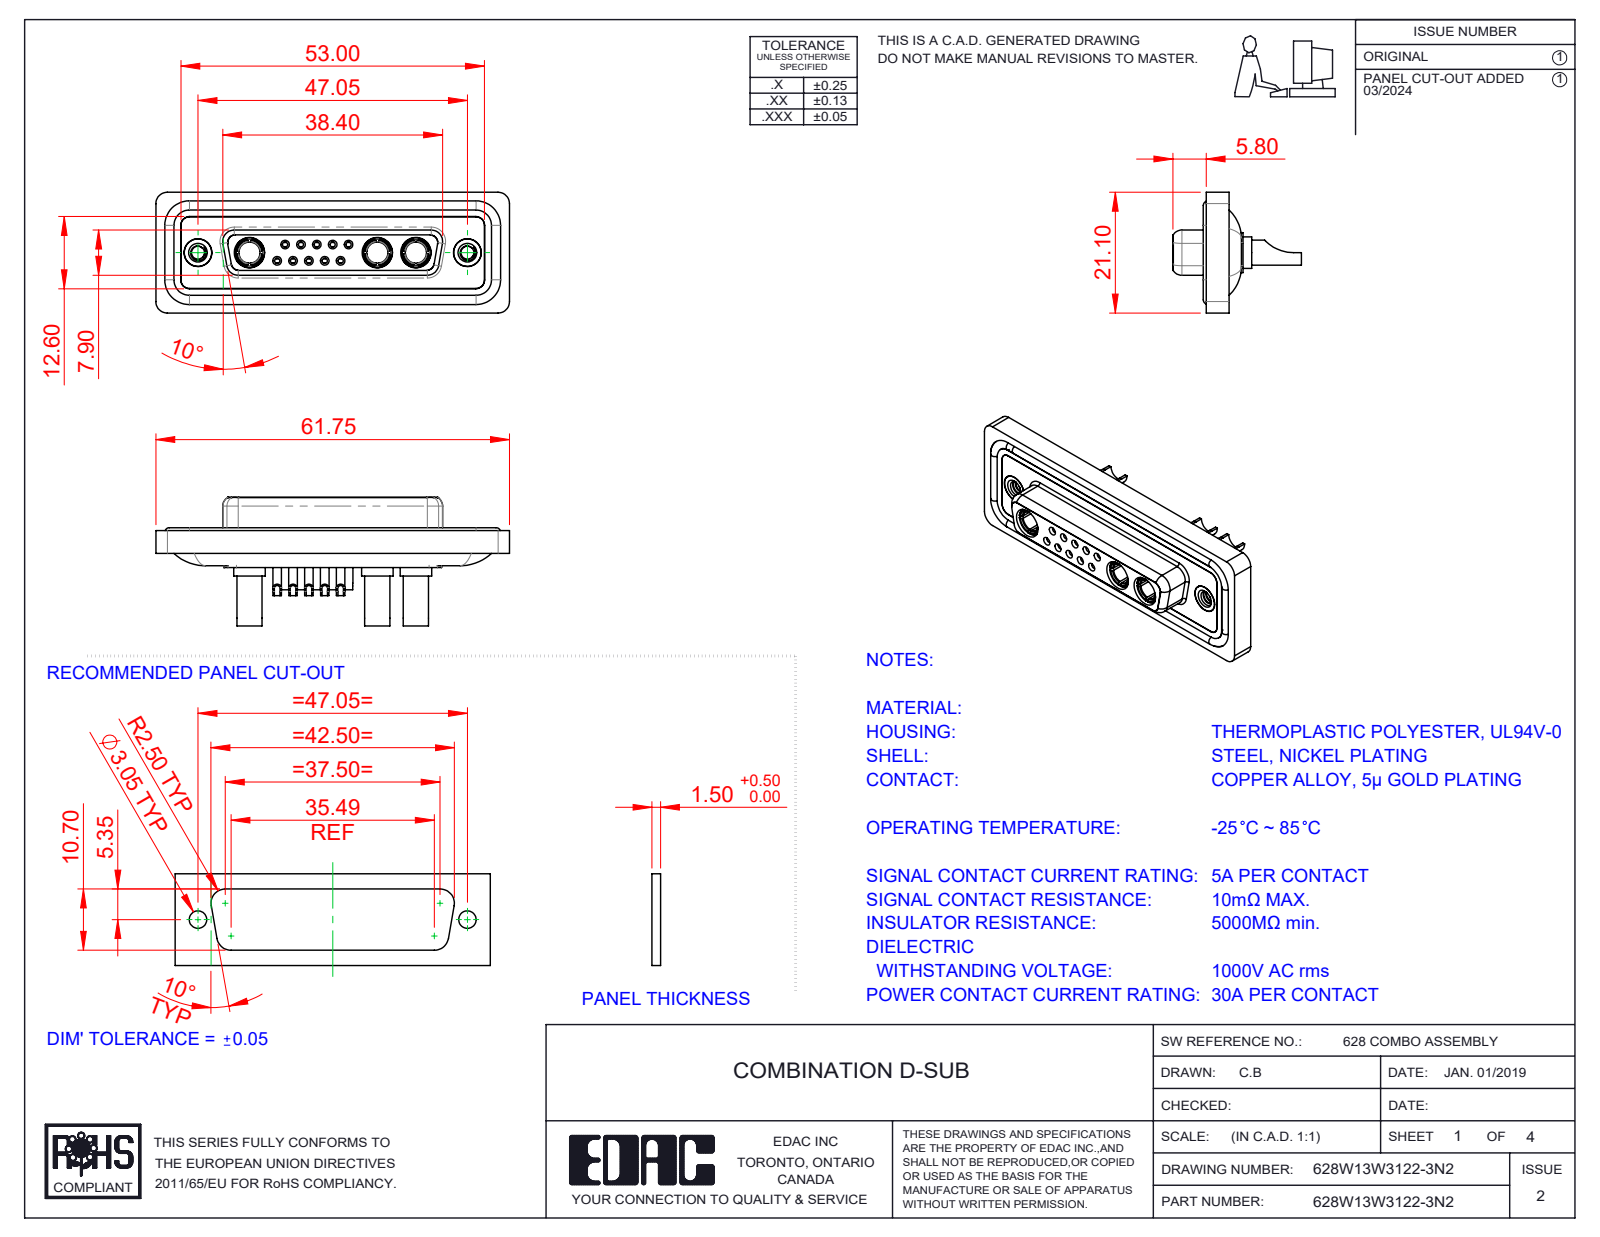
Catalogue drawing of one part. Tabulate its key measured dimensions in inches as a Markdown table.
| quantity | value |
| --- | --- |
| part name | 628Combo Shell Front_25 Contacts; 628Combo Shell Rear_25 Contacts; 628Combo Housing_13W3; 628Combo Threaded Rivet_2 (+5 more) |
| STEP written by | SolidWorks 2023 (CONFIG_CONTROL_DESIGN) |
| units | inches |
| bodies | 23 solids, 1176 faces (371 planar, 476 cylindrical, 329 other) |
| overall size | 2.431 × 0.884 × 0.831 |
| volume | 0.511 in³ |
| surface area | 21.91 in² |
| round holes (diameter × count) | 0.035 × 10, 0.039 × 10, 0.043 × 10, 0.059 × 10, 0.079 × 10, 0.063 × 5, 0.067 × 5, 0.191 × 5, 0.138 × 3, 0.146 × 3, 0.209 × 3, 0.089 × 2 |
| round bosses / shafts (diameter × count) | 0.087 × 10, 0.063 × 9, 0.217 × 3, 0.205 × 3, 0.195 × 3, 0.187 × 3, 0.173 × 3, 0.148 × 3 |
| partial cylindrical surfaces (radius × count) | 0.059 × 22, 0.079 × 18, 0.053 × 8, 0.063 × 8, 0.039 × 6, 0.01 × 4, 0.02 × 4, 0.024 × 4 |
| main face-to-face distances | 0.016, 0.071, 0.293, 0.222, 0.02, 0.26, 0.278, 0.063, 0.114, 0.043 |
| hole center spacings | 0.124, 0.109, 0.198, 0.198, 0.218, 0.327, 0.295, 0.109 |
